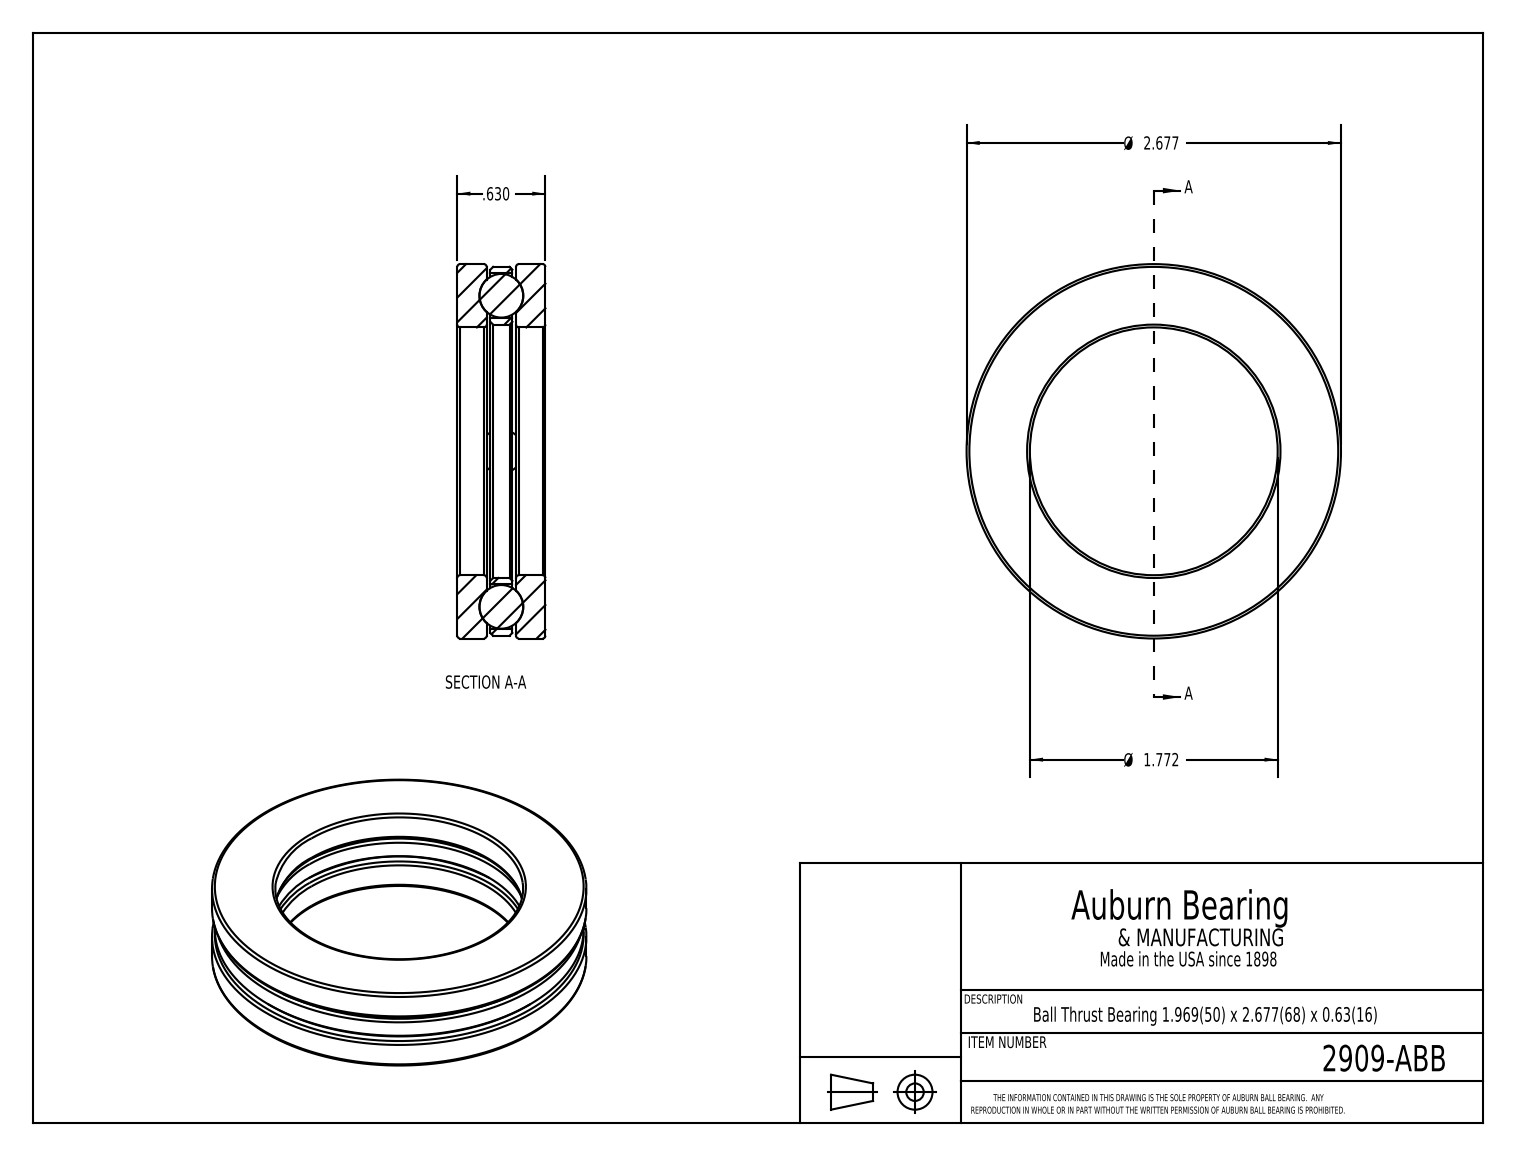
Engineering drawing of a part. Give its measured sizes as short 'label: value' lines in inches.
name: 2909-ABB
written by: SolidWorks 2017 (CONFIG_CONTROL_DESIGN)
unit: in
bodies: 7 solids, 34 faces (8 planar, 8 cylindrical, 18 other)
size: 2.677 × 2.677 × 0.63
volume: 1.367 in³; area: 24.1 in²
holes: 1× ⌀0.322, 1× ⌀1.969, 1× ⌀2.009
bosses: 1× ⌀2.677, 1× ⌀2.637
face distances: 0.236, 0.394, 0.63, 0.157, 0.21, 0.42, 0.026, 0.184, 0.21
hole spacings: 1.161
